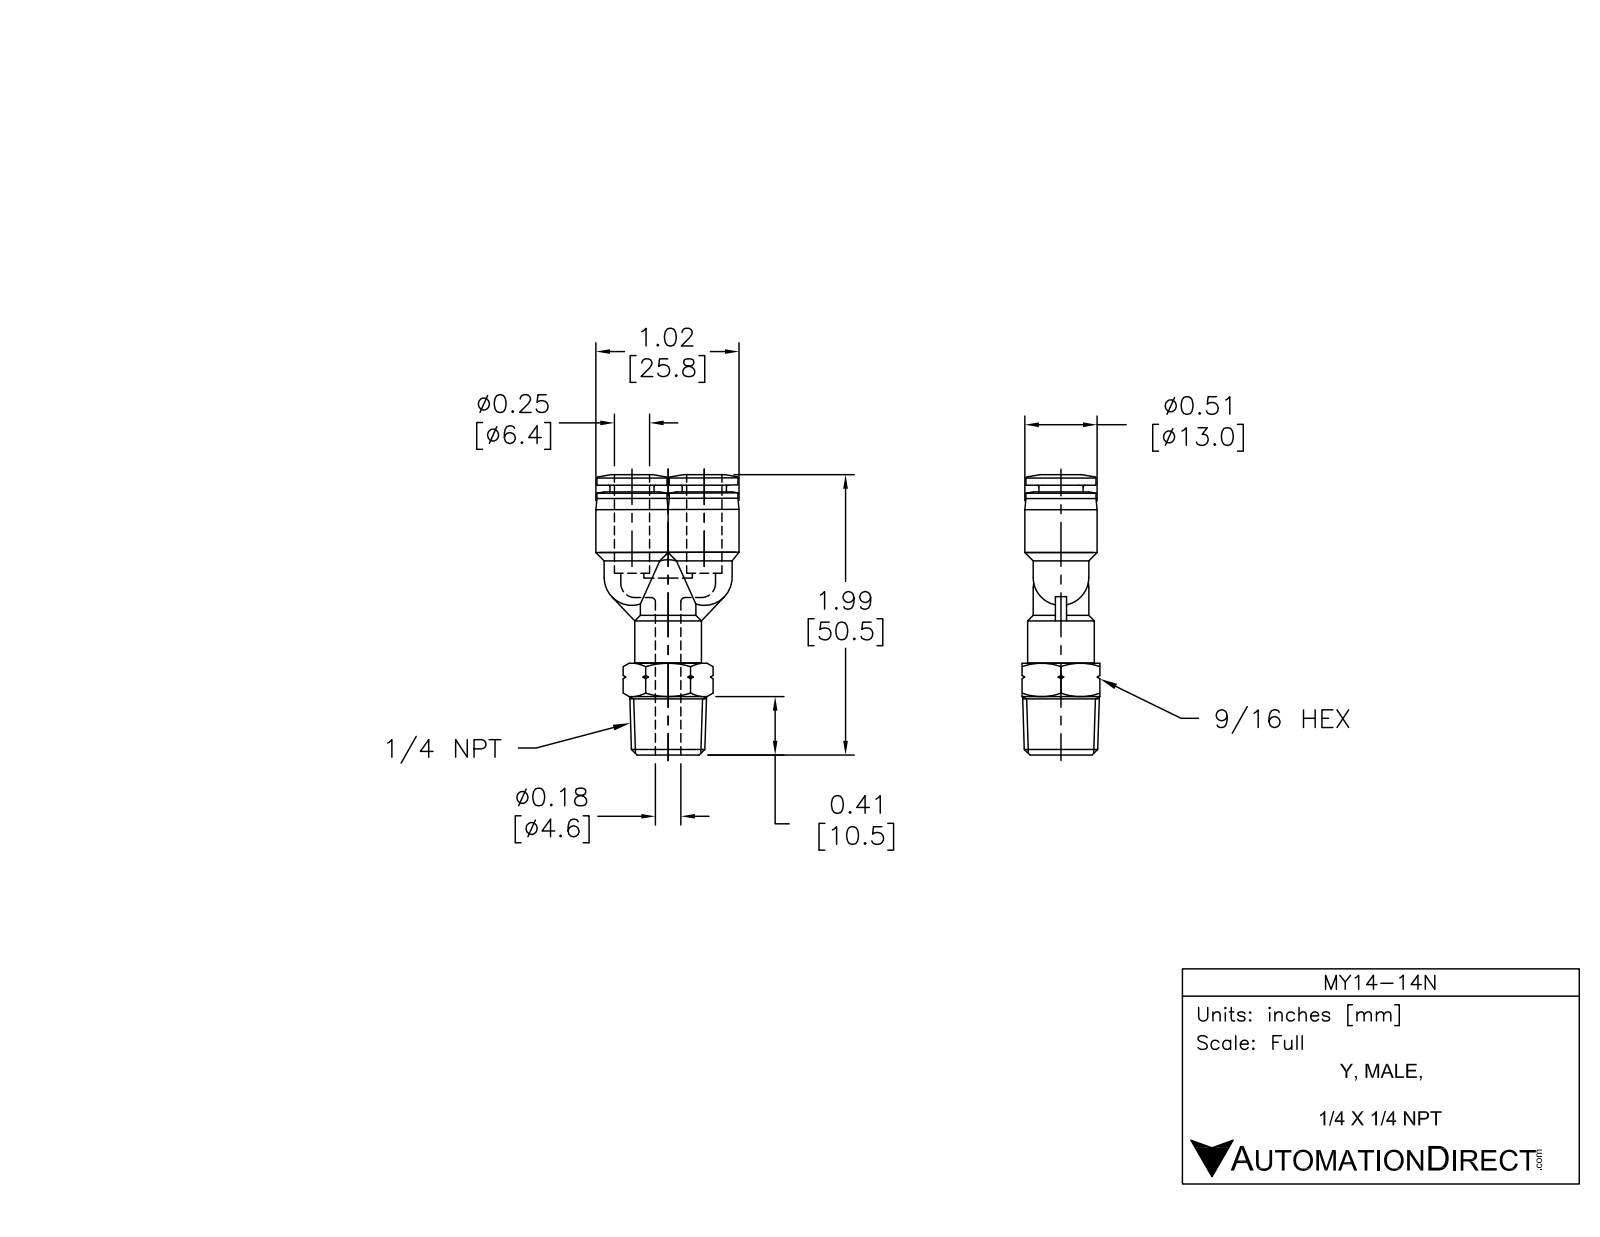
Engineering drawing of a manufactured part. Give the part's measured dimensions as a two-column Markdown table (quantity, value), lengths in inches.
| quantity | value |
| --- | --- |
| part name | MY14-14N |
| STEP written by | SolidWorks 2015 (AUTOMOTIVE_DESIGN) |
| units | inches |
| bodies | 1 solid, 126 faces (22 planar, 29 cylindrical, 75 other) |
| overall size | 1.984 × 1.024 × 0.551 |
| volume | 0.419 in³ |
| surface area | 7.425 in² |
| round holes (diameter × count) | 0.258 × 2, 0.177 × 1 |
| round bosses / shafts (diameter × count) | 0.394 × 3, 0.512 × 2, 0.496 × 2, 0.313 × 2, 0.472 × 1 |
| main face-to-face distances | 0.551, 1.909, 0.63, 0.047, 1.862, 0.236, 0.65, 1.213, 1.26, 0.315 |
| hole center spacings | 0.256, 0.512 |
